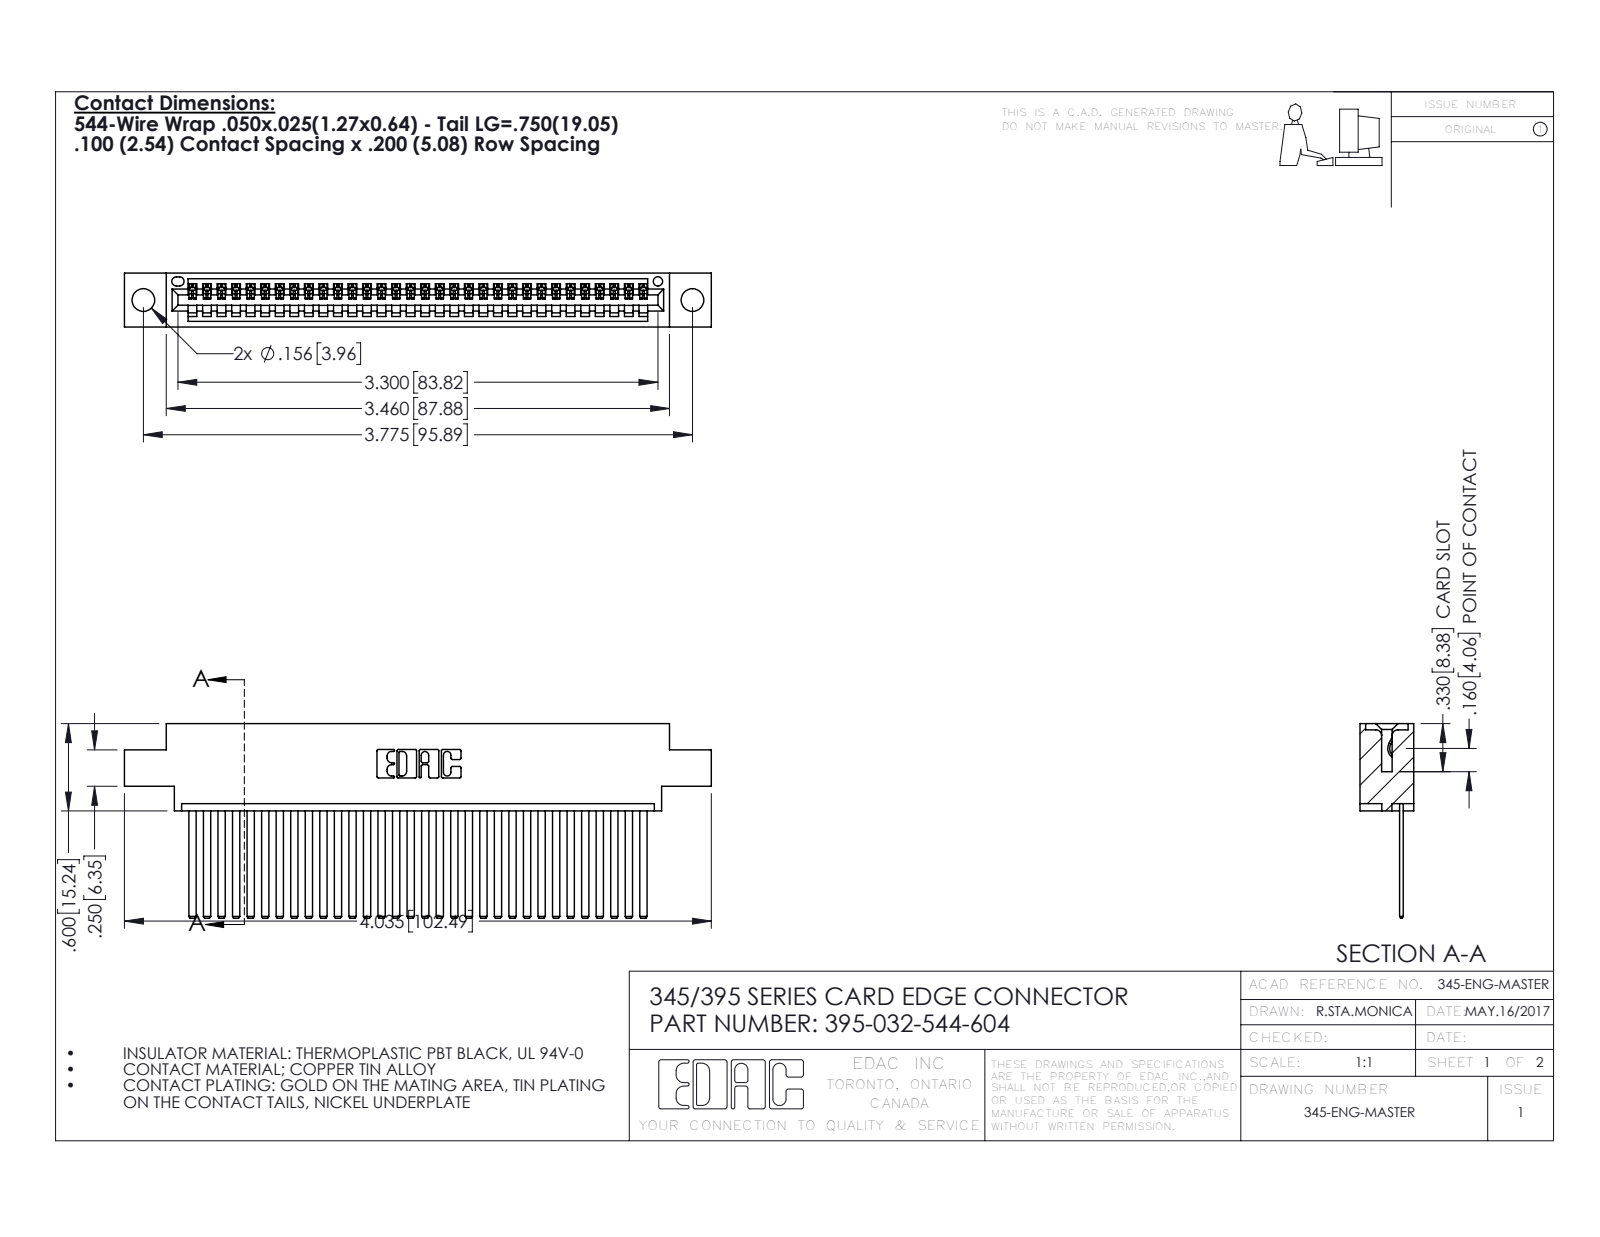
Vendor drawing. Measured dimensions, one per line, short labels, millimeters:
name: 395-032-544-604; 345-292-001_345-293-144; 345 Part_0.170 Offset - 0.156 Dia-TH
written by: SolidWorks 2016 (CONFIG_CONTROL_DESIGN)
unit: mm
bodies: 33 solids, 1794 faces (1236 planar, 558 cylindrical, 0 other)
size: 102.5 × 34 × 9.4
volume: 9 820 mm³; area: 13 960 mm²
holes: 2× ⌀4, 1× ⌀1.6
rounds: 64× R0.2, 22× R0.3, 6× R0.2, 6× R0.8, 3× R0.7, 2× R0.8, 2× R1, 1× R0.4
face distances: 1.8, 7.6, 0.6, 2.5, 6.9, 9.4, 5.1, 5.7, 4.4, 3.8
hole spacings: 6.9, 89.9, 95.9
